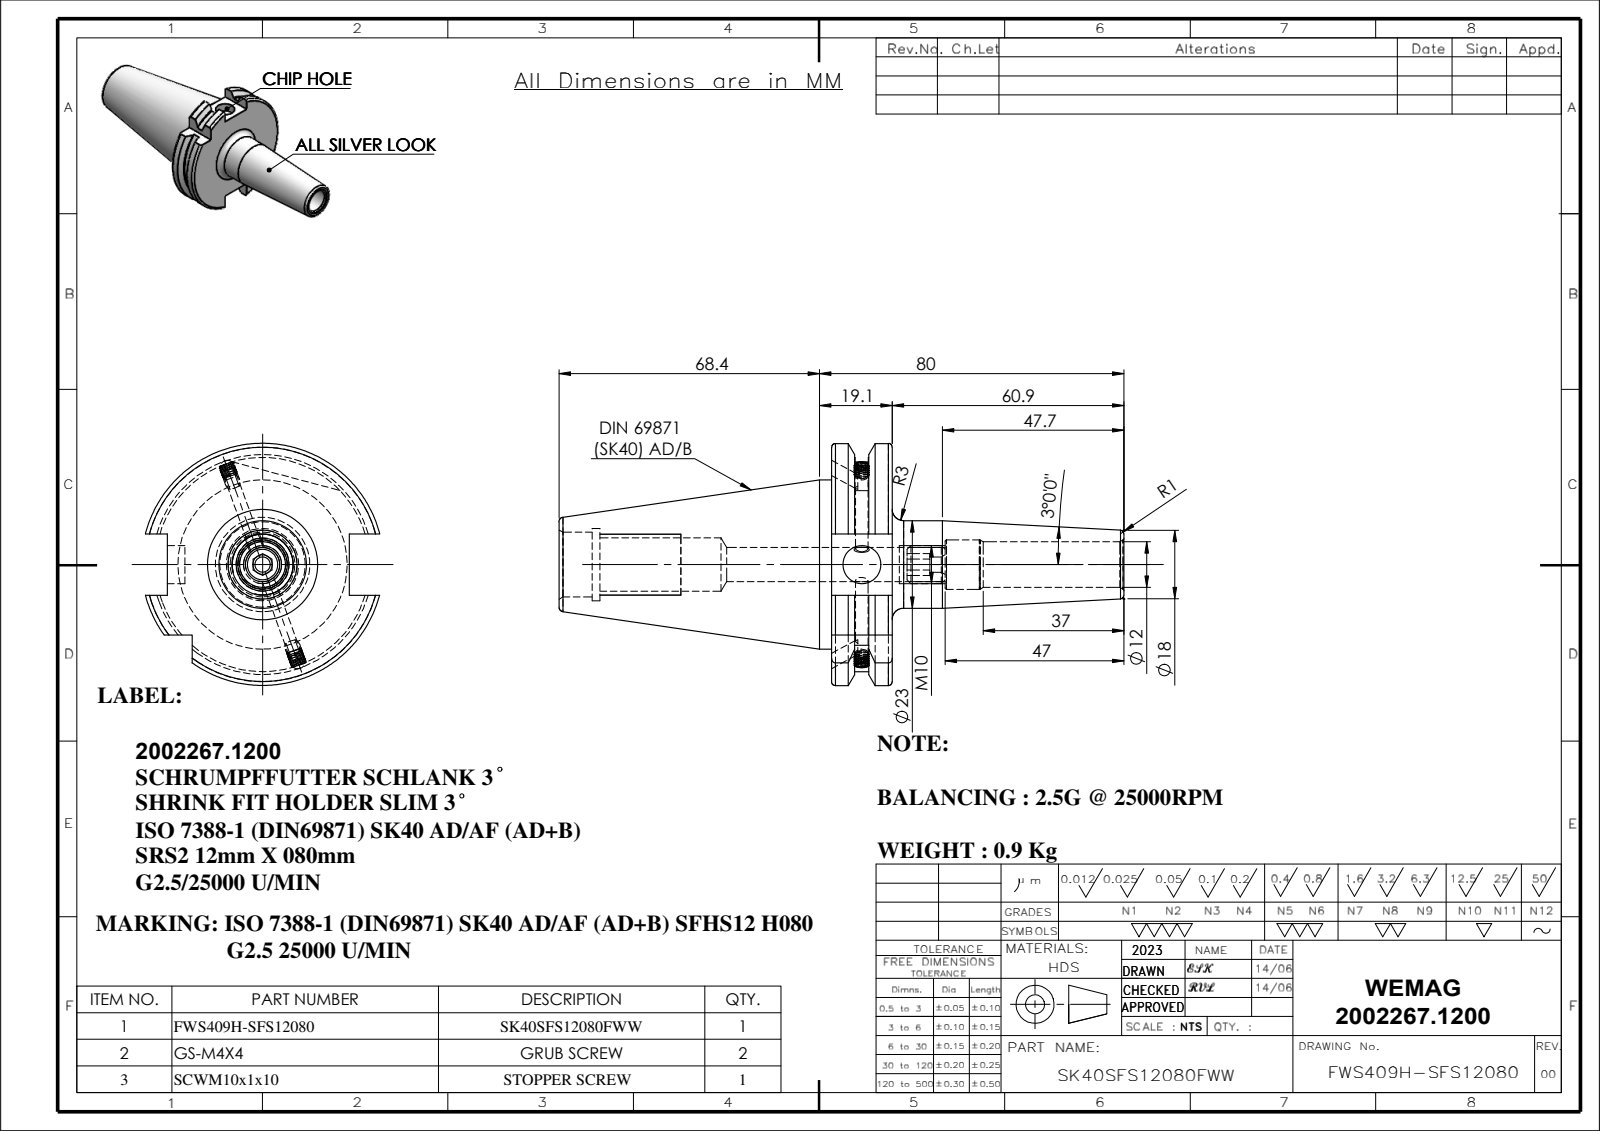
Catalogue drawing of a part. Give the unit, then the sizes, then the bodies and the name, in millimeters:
Units: millimetres
Overall size (bounding box): 148.4 × 63.55 × 61.48
Round holes (diameter × count): ⌀3.3 ×1, ⌀4 ×1, ⌀9 ×1, ⌀10 ×1, ⌀12 ×1, ⌀13 ×1, ⌀14 ×1, ⌀17 ×1, ⌀19 ×1
Round bosses / shafts (diameter × count): ⌀4 ×2, ⌀44.45 ×1, ⌀23 ×1, ⌀10 ×1
Partial cylindrical surfaces — rounded edges, fillets, slot ends (radius × count): R28.12 ×1, R31.77 ×1
Main face-to-face distances: 15.9, 60.9, 76.8, 16.1, 47.8, 71.6, 87.5, 10.7, 77.63, 66.93
Volume: 117 944 mm³ · Surface area: 27 464 mm²
Bodies: 4 solids, 220 faces (56 planar, 58 cylindrical, 106 other)
Part name (STEP PRODUCT): SK40SFS12080FWW; GS-M4X4_DIN 913 - M4 x 4-N; SCWM10X1-10; 91406-SRS212080
STEP written by: SolidWorks 2018 (CONFIG_CONTROL_DESIGN)
